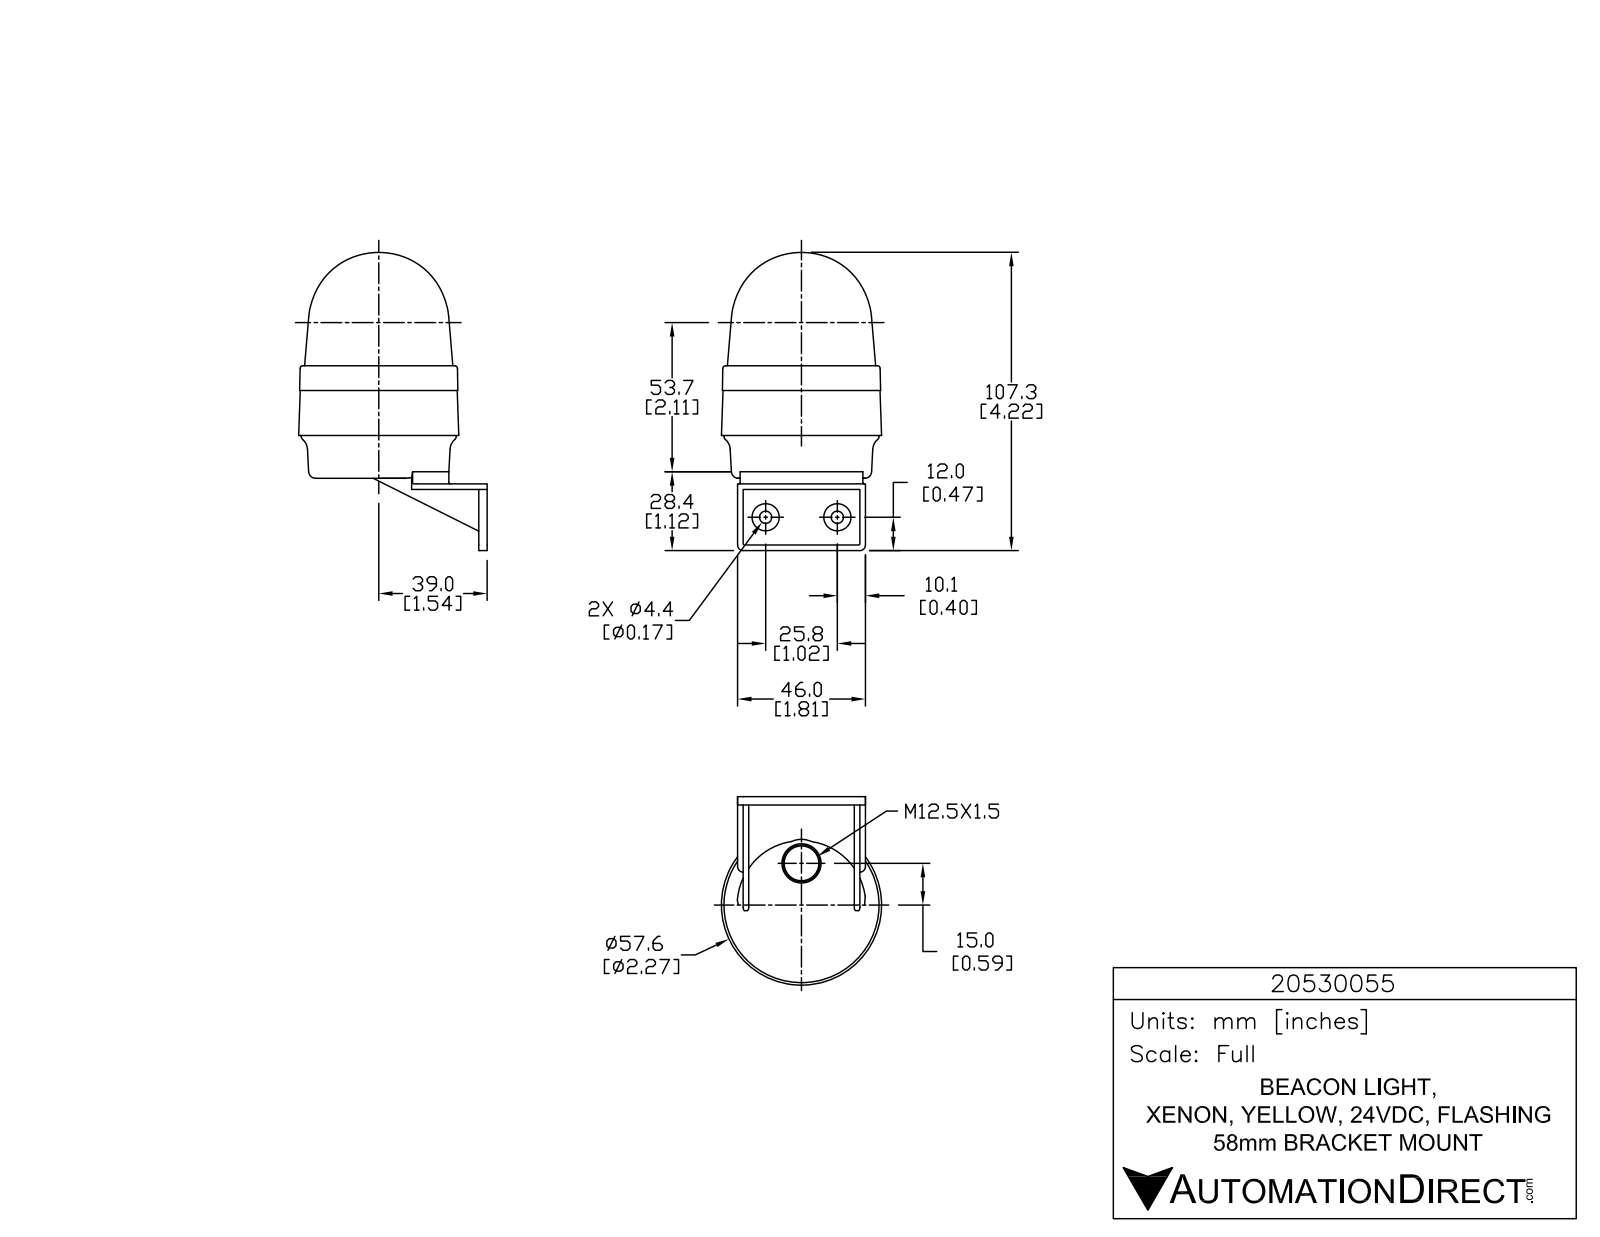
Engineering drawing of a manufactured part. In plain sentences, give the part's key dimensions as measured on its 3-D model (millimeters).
The part is named "20530055". Its 3-D file was written by "SolidWorks 2015 (AUTOMOTIVE_DESIGN)". It is 1 solid with 828 faces: 551 planar, 179 cylindrical and 98 other. Overall it measures 107.3 by 72.4 by 61.1 millimeters. Its volume is 168 300 cubic millimeters and its surface area 21 540 square millimeters. Round holes: 3 of diameter 1, 2 of diameter 4.4. Round bosses or shafts: 3 of diameter 5.7, 3 of diameter 1.4, 2 of diameter 9.8, 1 of diameter 55.8. Partial cylindrical surfaces (rounded edges, fillets, slot ends): 6 of radius 0.2, 6 of radius 0.2, 6 of radius 0.2, 6 of radius 0.5, 6 of radius 3.3, 4 of radius 2, 3 of radius 0.1, 3 of radius 0.1. The main face-to-face distances are 2, 4, 40, 42, 1, 3, 38, 22, 24, 19.4. The hole center spacings are 25.8.
